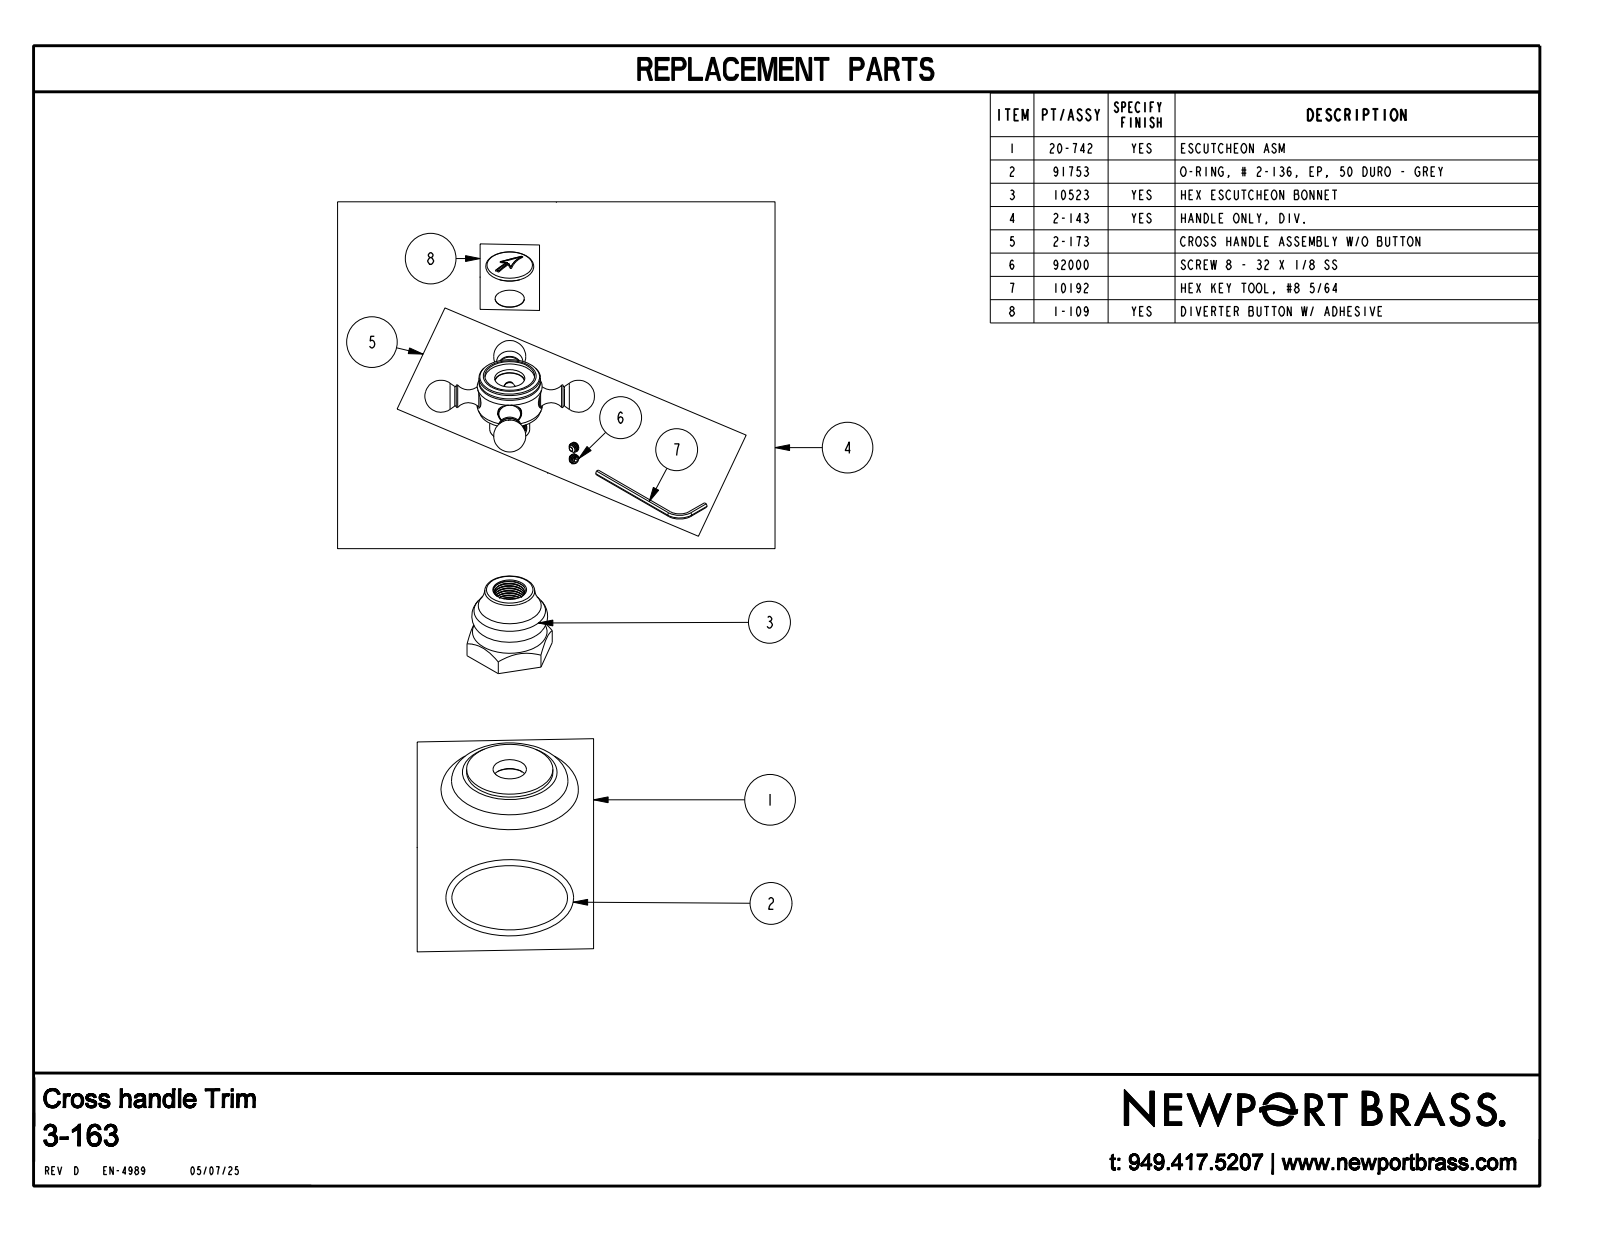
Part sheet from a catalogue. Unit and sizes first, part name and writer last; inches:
Units: inches
Overall size (bounding box): 2.909 × 2.36 × 2.36
Round holes (diameter × count): ⌀0.855 ×1
Round bosses / shafts (diameter × count): ⌀1.482 ×1, ⌀1.055 ×1, ⌀0.687 ×1
Partial cylindrical surfaces — rounded edges, fillets, slot ends (radius × count): R0.015 ×2, R0.196 ×2, R1 ×2, R1.02 ×2, R0.02 ×1
Main face-to-face distances: 1.687, 1.313, 0.02, 1.707, 0.375, 1.312, 1.332, 1.313, 0.437, 0.062
Volume: 4.126 in³ · Surface area: 24.88 in²
Bodies: 2 solids, 152 faces (39 planar, 23 cylindrical, 90 other)
Part name (STEP PRODUCT): 3-163
STEP written by: CREO PARAMETRIC BY PTC INC, 2023134 (CONFIG_CONTROL_DESIGN)
